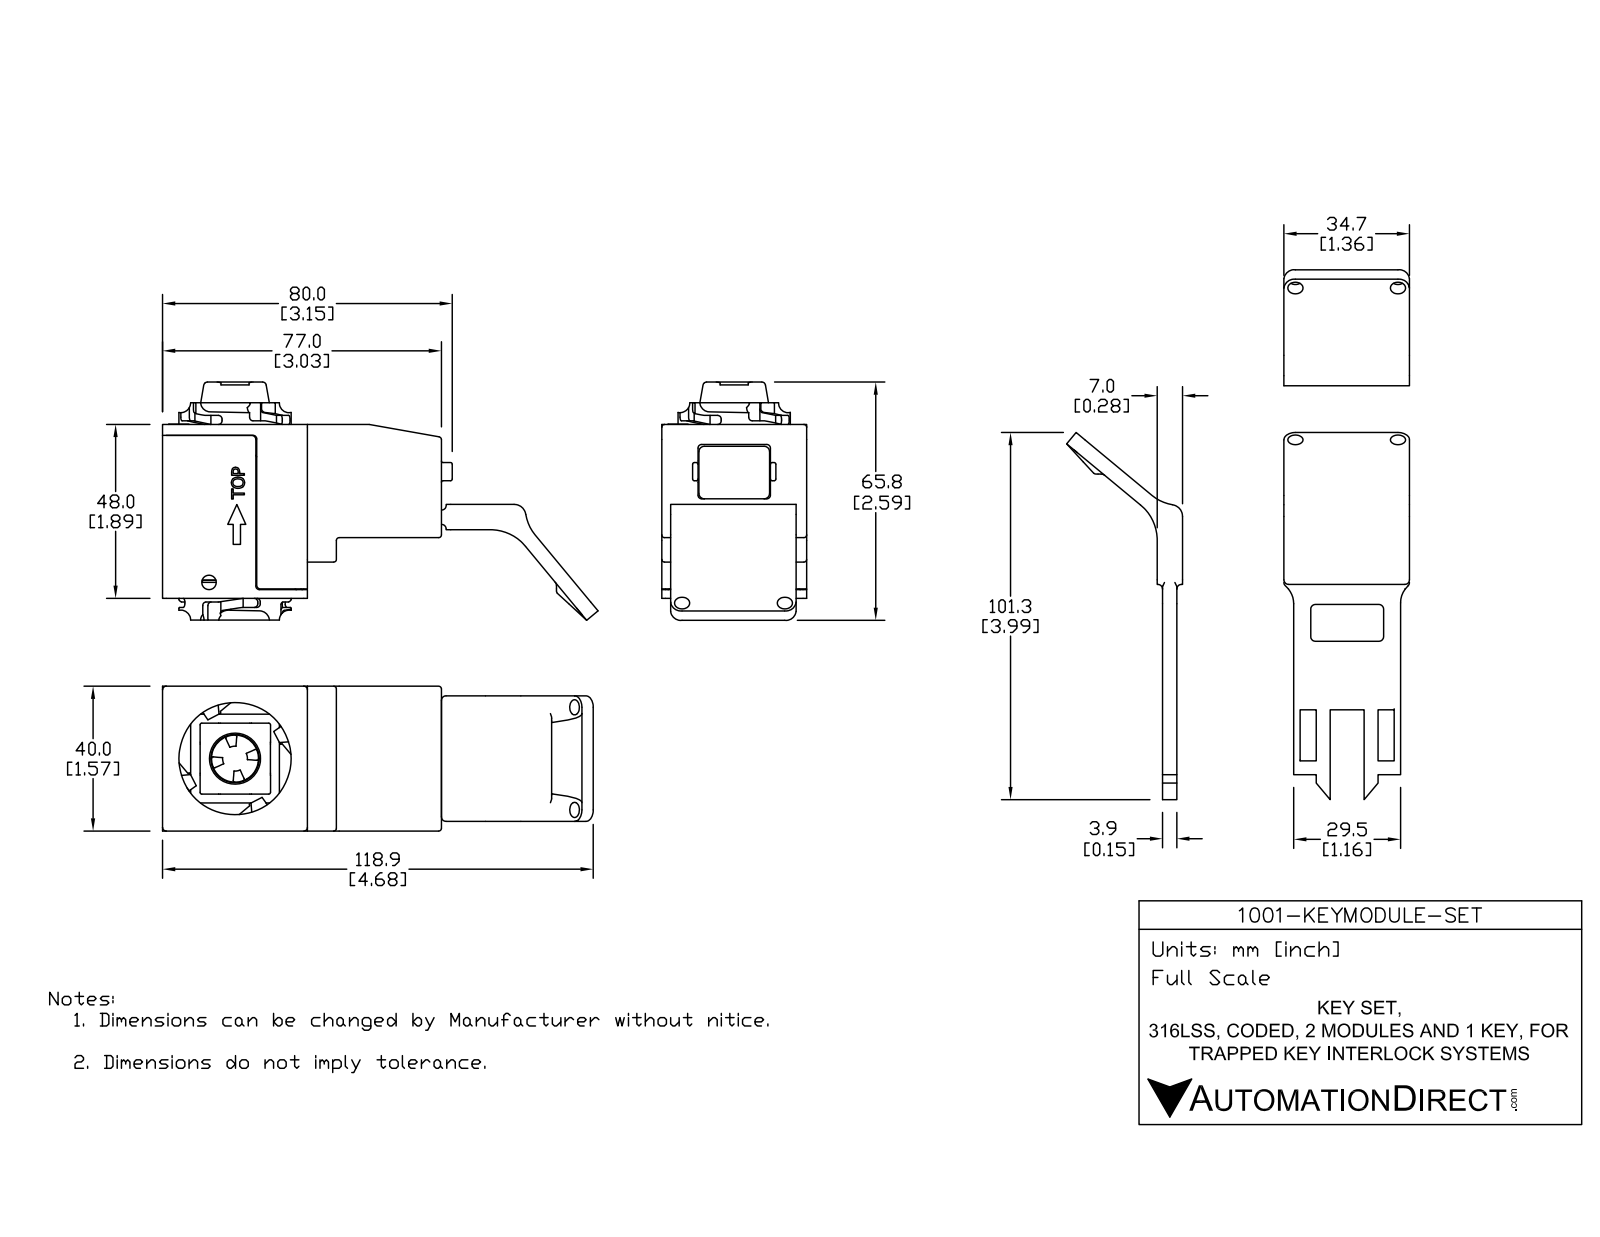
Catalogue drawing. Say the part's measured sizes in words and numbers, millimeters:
The part is named "ST2331_Endteil_M_1; ST2131_10_1; 1001-KEYMODULE-SET; ST2330_Bajonett_1 (+2 more)". Its 3-D file was written by "SolidWorks 2017 (AUTOMOTIVE_DESIGN)". It is 11 solids with 3467 faces: 1460 planar, 579 cylindrical and 1428 other. Overall it measures 131 by 116.7 by 80 millimeters. Its volume is 328 200 cubic millimeters and its surface area 66 390 square millimeters. Round holes: 5 of diameter 4, 2 of diameter 2, 2 of diameter 2.5, 2 of diameter 5.5, 1 of diameter 3.4, 1 of diameter 10. Round bosses or shafts: 1 of diameter 10, 1 of diameter 4.1. Partial cylindrical surfaces (rounded edges, fillets, slot ends): 249 of radius 0.5, 61 of radius 1, 46 of radius 0.2, 32 of radius 0.5, 29 of radius 0.8, 15 of radius 2, 10 of radius 5.5, 8 of radius 2.7. The main face-to-face distances are 76.5, 40, 48, 20, 36.5, 116.5, 68, 31.2, 36.8, 16.7. The hole center spacings are 14.5, 76.5, 19.6, 20.5, 20.5, 24.5, 26.7, 29.8.
